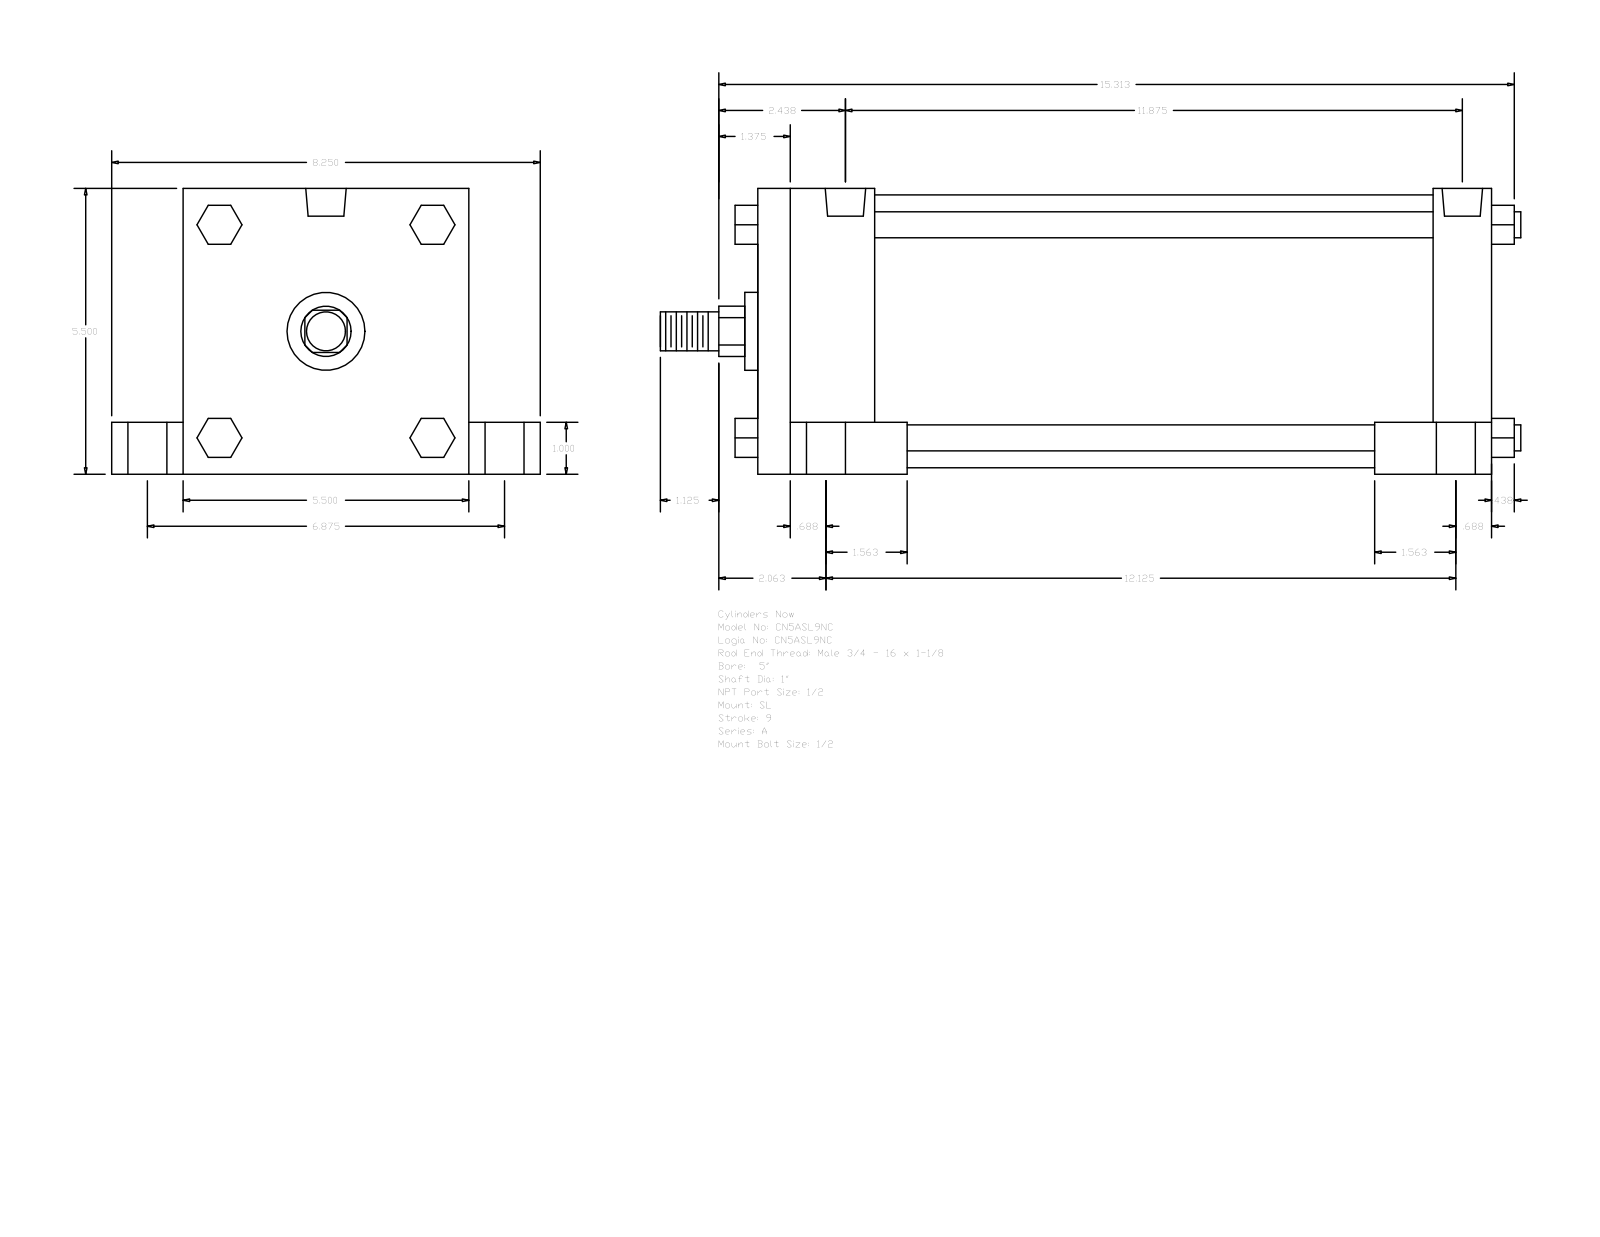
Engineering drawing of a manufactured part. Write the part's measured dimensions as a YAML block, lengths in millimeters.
part_name: "A_SL__0500_1"
step_written_by: "GSSL Pune (CONFIG_CONTROL_DESIGN)"
units: millimeters
bodies: {solids: 0, faces: 150, planar: 114, cylindrical: 36, other: 0}
overall_size: [420.69, 209.55, 139.7]
round_holes:
  - {diameter: 8.73, count: 4}
  - {diameter: 19.05, count: 4}
  - {diameter: 25.4, count: 4}
  - {diameter: 19.77, count: 2}
round_bosses_or_shafts:
  - {diameter: 12.7, count: 4}
  - {diameter: 133.35, count: 1}
  - {diameter: 38.1, count: 1}
  - {diameter: 25.4, count: 1}
  - {diameter: 19.05, count: 1}
partial_cylinders:
  - {radius: 12.29, count: 1}
face_to_face_distances: [139.7, 358.77, 28.57, 25.4, 114.3, 34.93, 174.63, 57.15, 330.2, 273.05]
hole_center_spacings: [2.39, 87.31, 87.37, 87.83, 88.12, 174.62, 296.85, 299.24]
